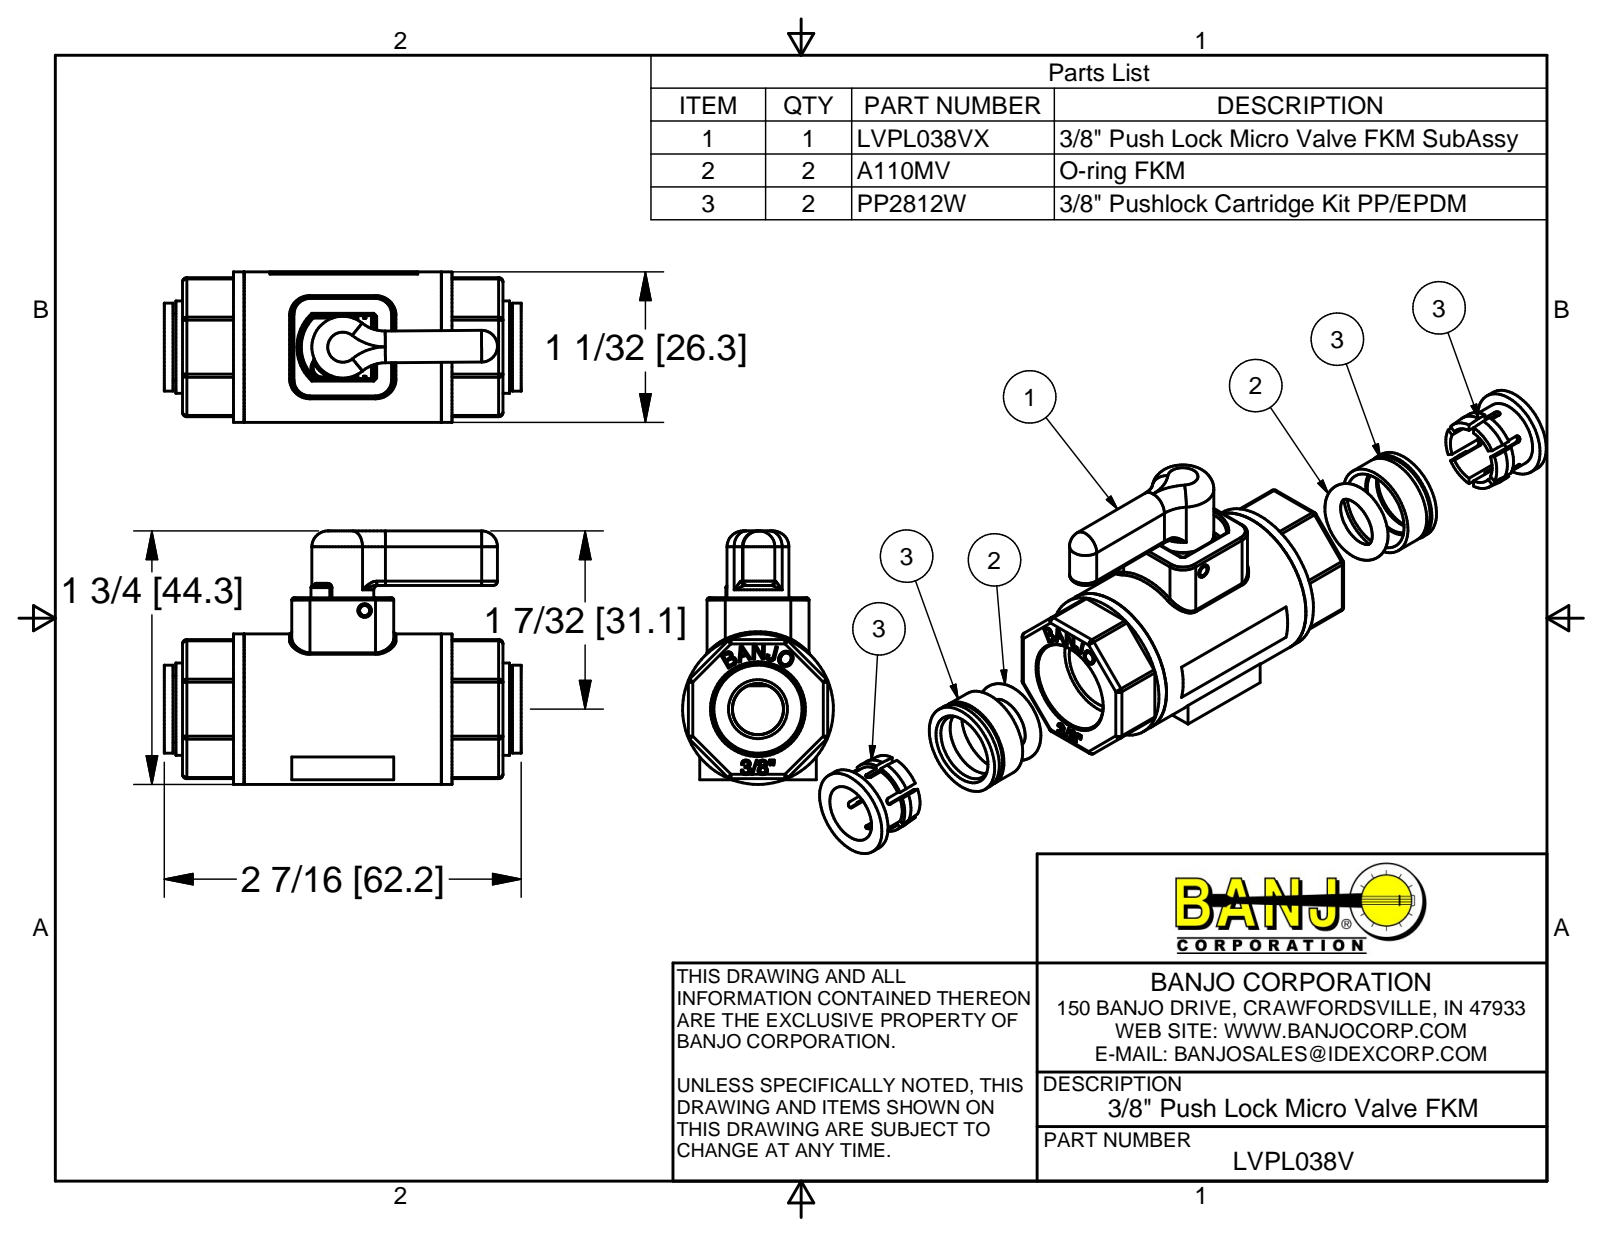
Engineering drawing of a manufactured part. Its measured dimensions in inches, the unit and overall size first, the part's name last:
Units: inches
Overall size (bounding box): 2.45 × 1.743 × 1.035
Round holes (diameter × count): ⌀0.093 ×1, ⌀0.251 ×1, ⌀0.35 ×1, ⌀0.366 ×1, ⌀0.37 ×1, ⌀0.376 ×1, ⌀0.38 ×1, ⌀0.405 ×1, ⌀0.421 ×1, ⌀0.47 ×1, ⌀0.547 ×1, ⌀0.632 ×1
Round bosses / shafts (diameter × count): ⌀1.035 ×1, ⌀0.845 ×1, ⌀0.812 ×1, ⌀0.785 ×1, ⌀0.635 ×1, ⌀0.63 ×1, ⌀0.605 ×1, ⌀0.6 ×1
Partial cylindrical surfaces — rounded edges, fillets, slot ends (radius × count): R0.03 ×26, R0.01 ×16, R0.015 ×14, R0.022 ×6, R0.125 ×4, R0.05 ×2, R0.109 ×2, R0.25 ×2
Main face-to-face distances: 0.977, 0.956, 0.377, 0.8, 0.05, 0.423, 1.4, 1.777, 0.327, 0.6
Volume: 1.762 in³ · Surface area: 35.49 in²
Bodies: 18 solids, 835 faces (344 planar, 181 cylindrical, 310 other)
Part name (STEP PRODUCT): LV03254A; AQ010V; LV02153B; LEV03255 (+8 more)
STEP written by: Autodesk Inventor 2014 (AUTOMOTIVE_DESIGN)
